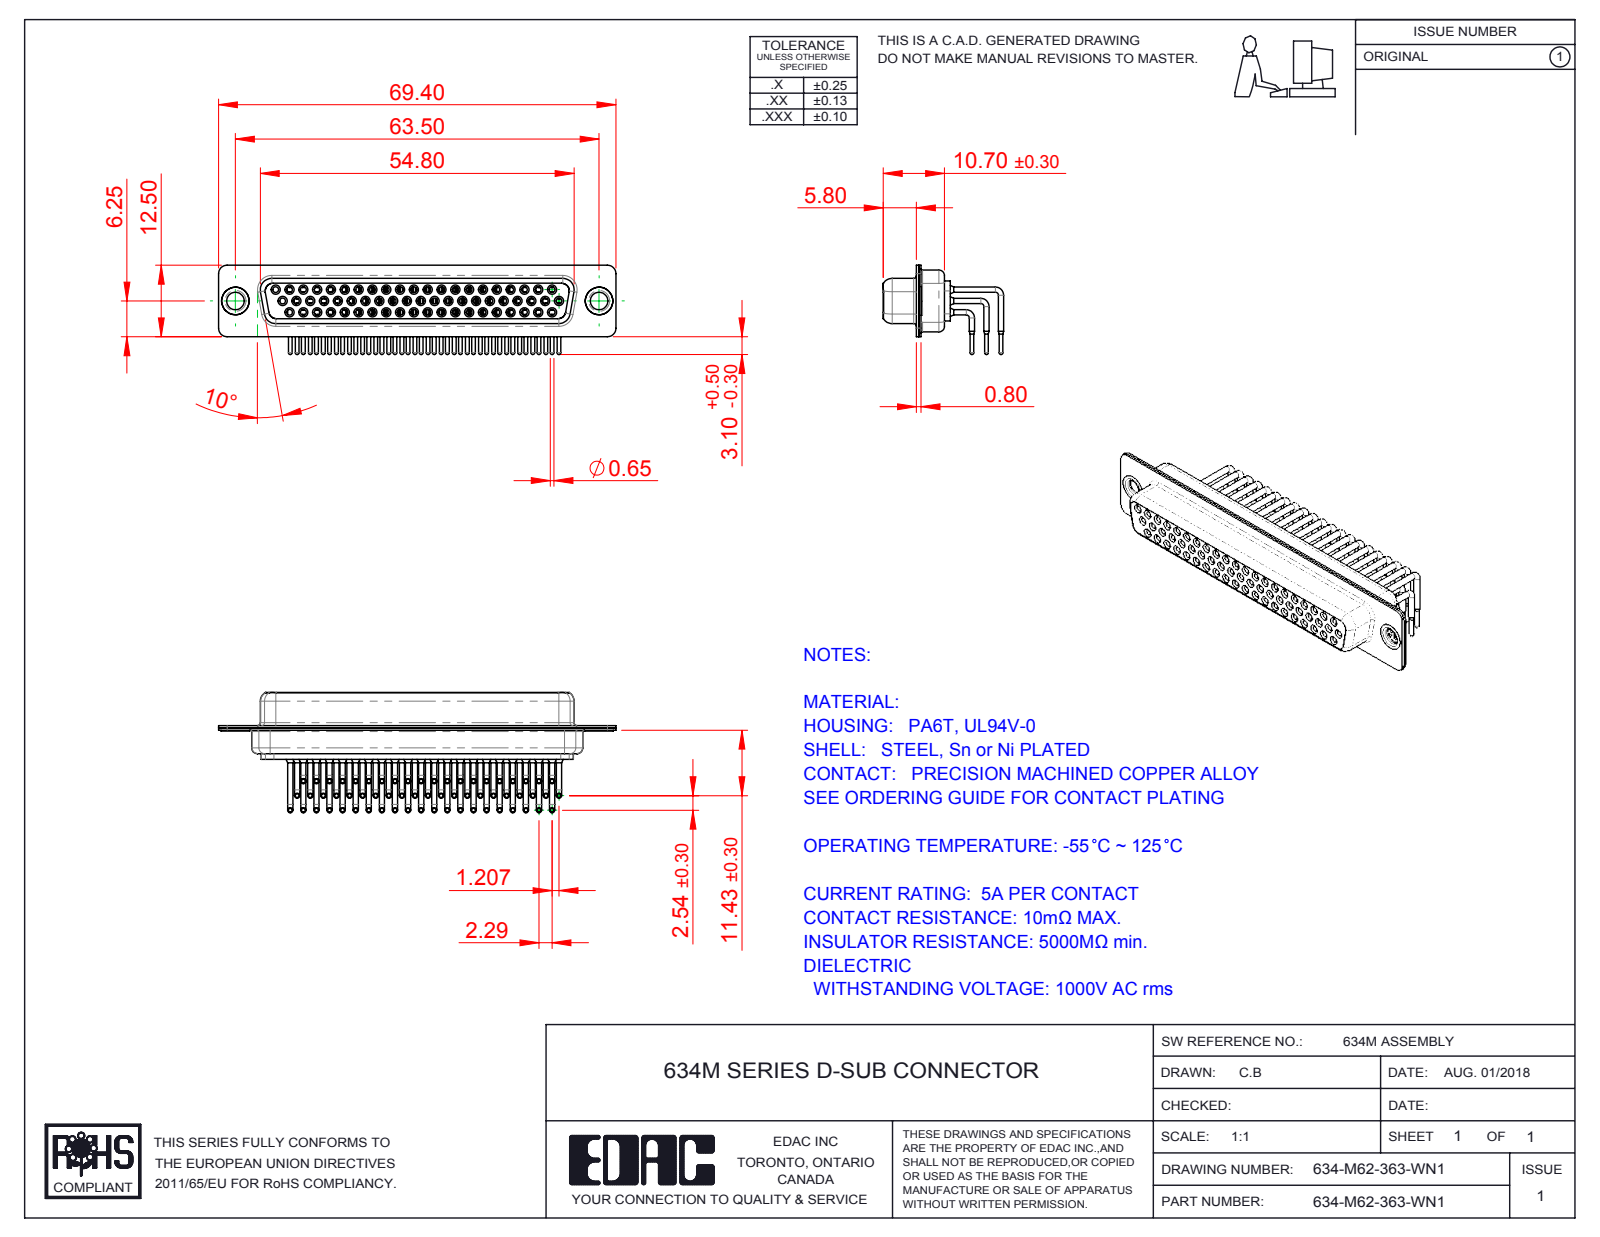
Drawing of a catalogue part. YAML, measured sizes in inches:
part_name: "634M Thru Hole Rivet; 634M Shell Rear_62 Contacts; 634M Housing_62 Contacts; 634M Shell Front_62 Contacts (+4 more)"
step_written_by: "SolidWorks 2016 (CONFIG_CONTROL_DESIGN)"
units: inches
bodies: {solids: 67, faces: 3539, planar: 997, cylindrical: 1547, other: 995}
overall_size: [2.732, 0.828, 0.614]
volume: 0.325
surface_area: 27.46
round_holes:
  - {diameter: 0.039, count: 62}
  - {diameter: 0.043, count: 62}
  - {diameter: 0.067, count: 62}
  - {diameter: 0.071, count: 62}
  - {diameter: 0.079, count: 62}
  - {diameter: 0.12, count: 2}
  - {diameter: 0.157, count: 2}
  - {diameter: 0.189, count: 2}
round_bosses_or_shafts:
  - {diameter: 0.035, count: 124}
  - {diameter: 0.063, count: 62}
  - {diameter: 0.059, count: 62}
  - {diameter: 0.026, count: 62}
  - {diameter: 0.079, count: 56}
  - {diameter: 0.197, count: 2}
  - {diameter: 0.193, count: 2}
  - {diameter: 0.14, count: 2}
partial_cylinders:
  - {radius: 0.059, count: 16}
  - {radius: 0.079, count: 12}
  - {radius: 0.053, count: 8}
  - {radius: 0.063, count: 8}
  - {radius: 0.01, count: 4}
  - {radius: 0.02, count: 4}
  - {radius: 0.024, count: 4}
  - {radius: 0.026, count: 4}
face_to_face_distances: [0.016, 0.057, 0.352, 0.075, 0.335, 0.091, 0.244, 0.018, 0.278, 0.033]
hole_center_spacings: [0.285, 0.091, 0.095, 0.38, 0.163, 0.19, 0.665, 0.57]
